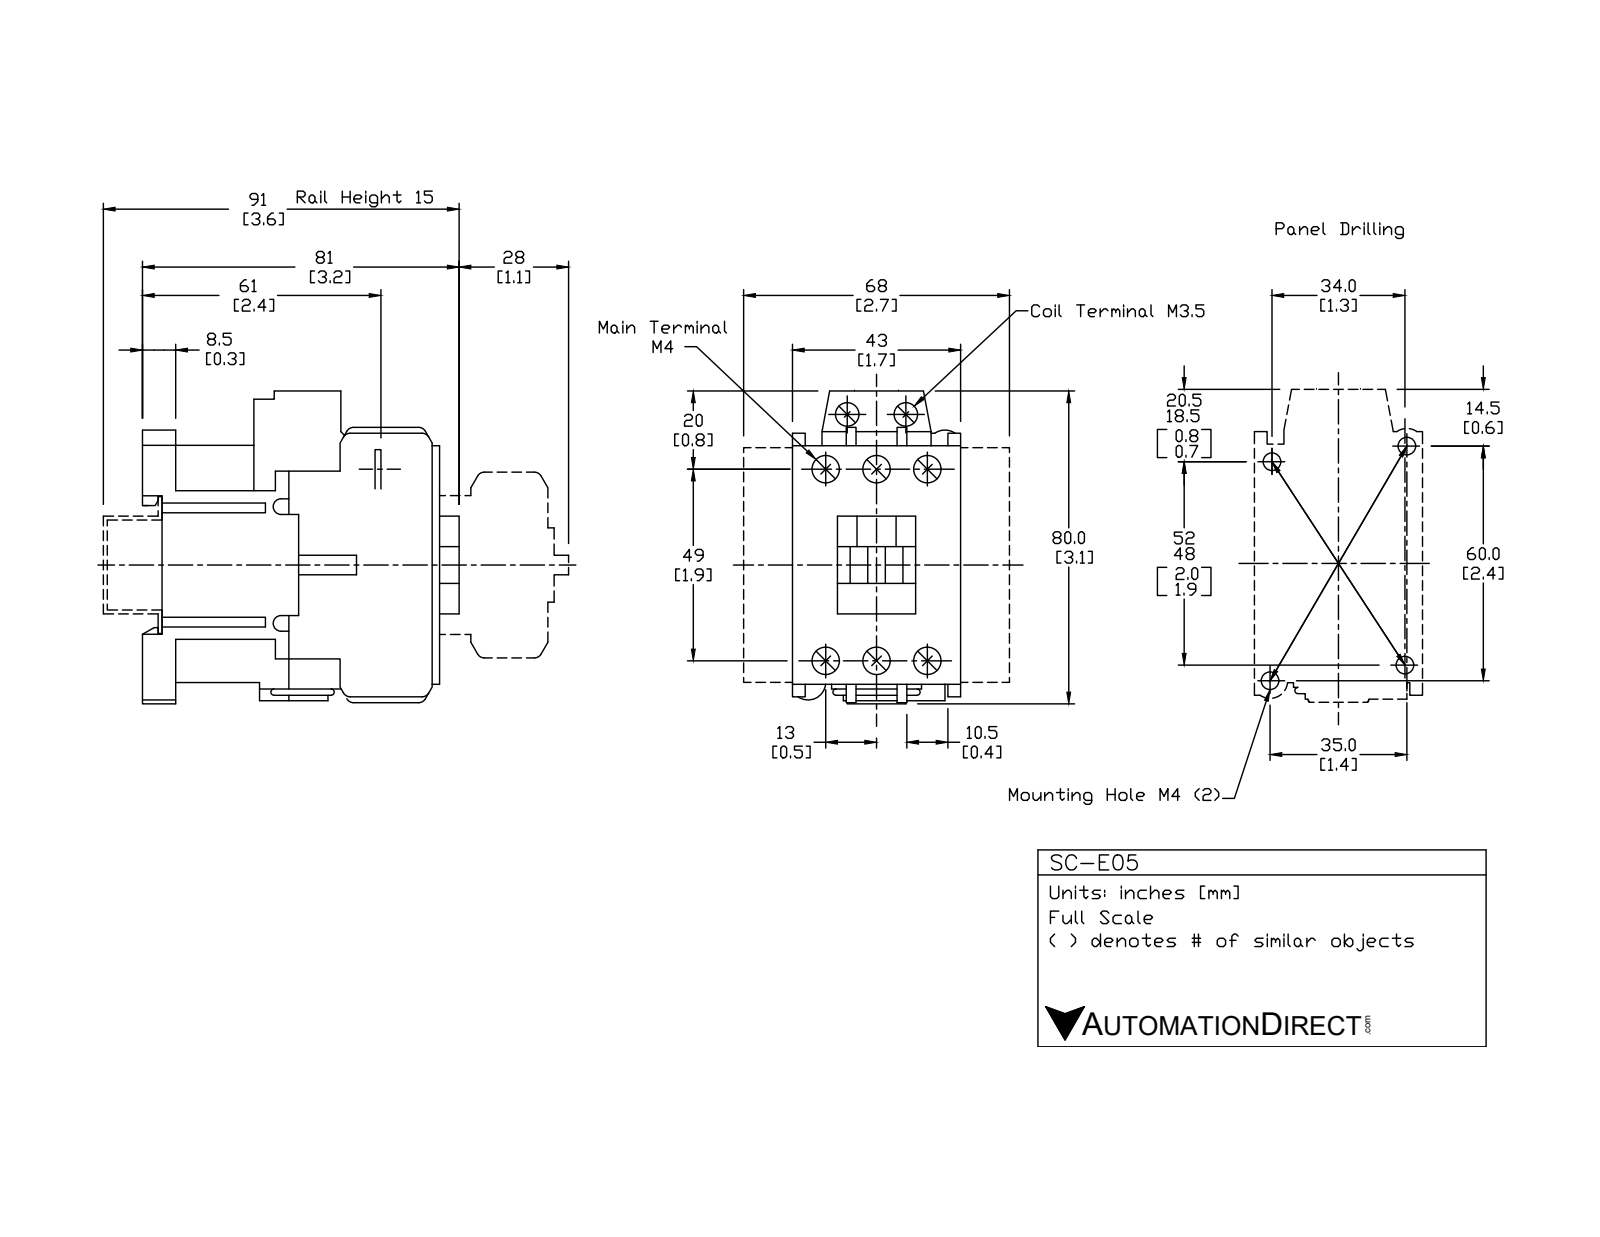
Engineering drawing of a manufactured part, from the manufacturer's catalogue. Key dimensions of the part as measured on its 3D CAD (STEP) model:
Part name (STEP PRODUCT): SC-E05-440VAC
STEP written by: SolidWorks 2015 (AUTOMOTIVE_DESIGN)
Units: inches
Bodies: 1 solid, 1388 faces (1148 planar, 192 cylindrical, 48 other)
Overall size (bounding box): 3.189 × 3.189 × 1.693
Volume: 9.981 in³ · Surface area: 65.66 in²
Round holes (diameter × count): ⌀0.161 ×6, ⌀0.276 ×6, ⌀0.142 ×2, ⌀0.177 ×2, ⌀0.264 ×2, ⌀0.063 ×1
Round bosses / shafts (diameter × count): ⌀0.299 ×6, ⌀0.157 ×6, ⌀0.28 ×2, ⌀0.26 ×2, ⌀0.138 ×2
Partial cylindrical surfaces — rounded edges, fillets, slot ends (radius × count): R0.059 ×32, R0.079 ×14, R0.02 ×10, R0.024 ×4, R0.089 ×4, R0.14 ×4, R0.163 ×2, R0.177 ×2
Main face-to-face distances: 1.693, 0.512, 0.413, 0.098, 0.925, 1.299, 0.64, 1.053, 0.61, 0.541
Hole centre spacings: 0.512, 1.996, 1.929, 0.28, 0.301, 0.592, 0.625, 0.709
